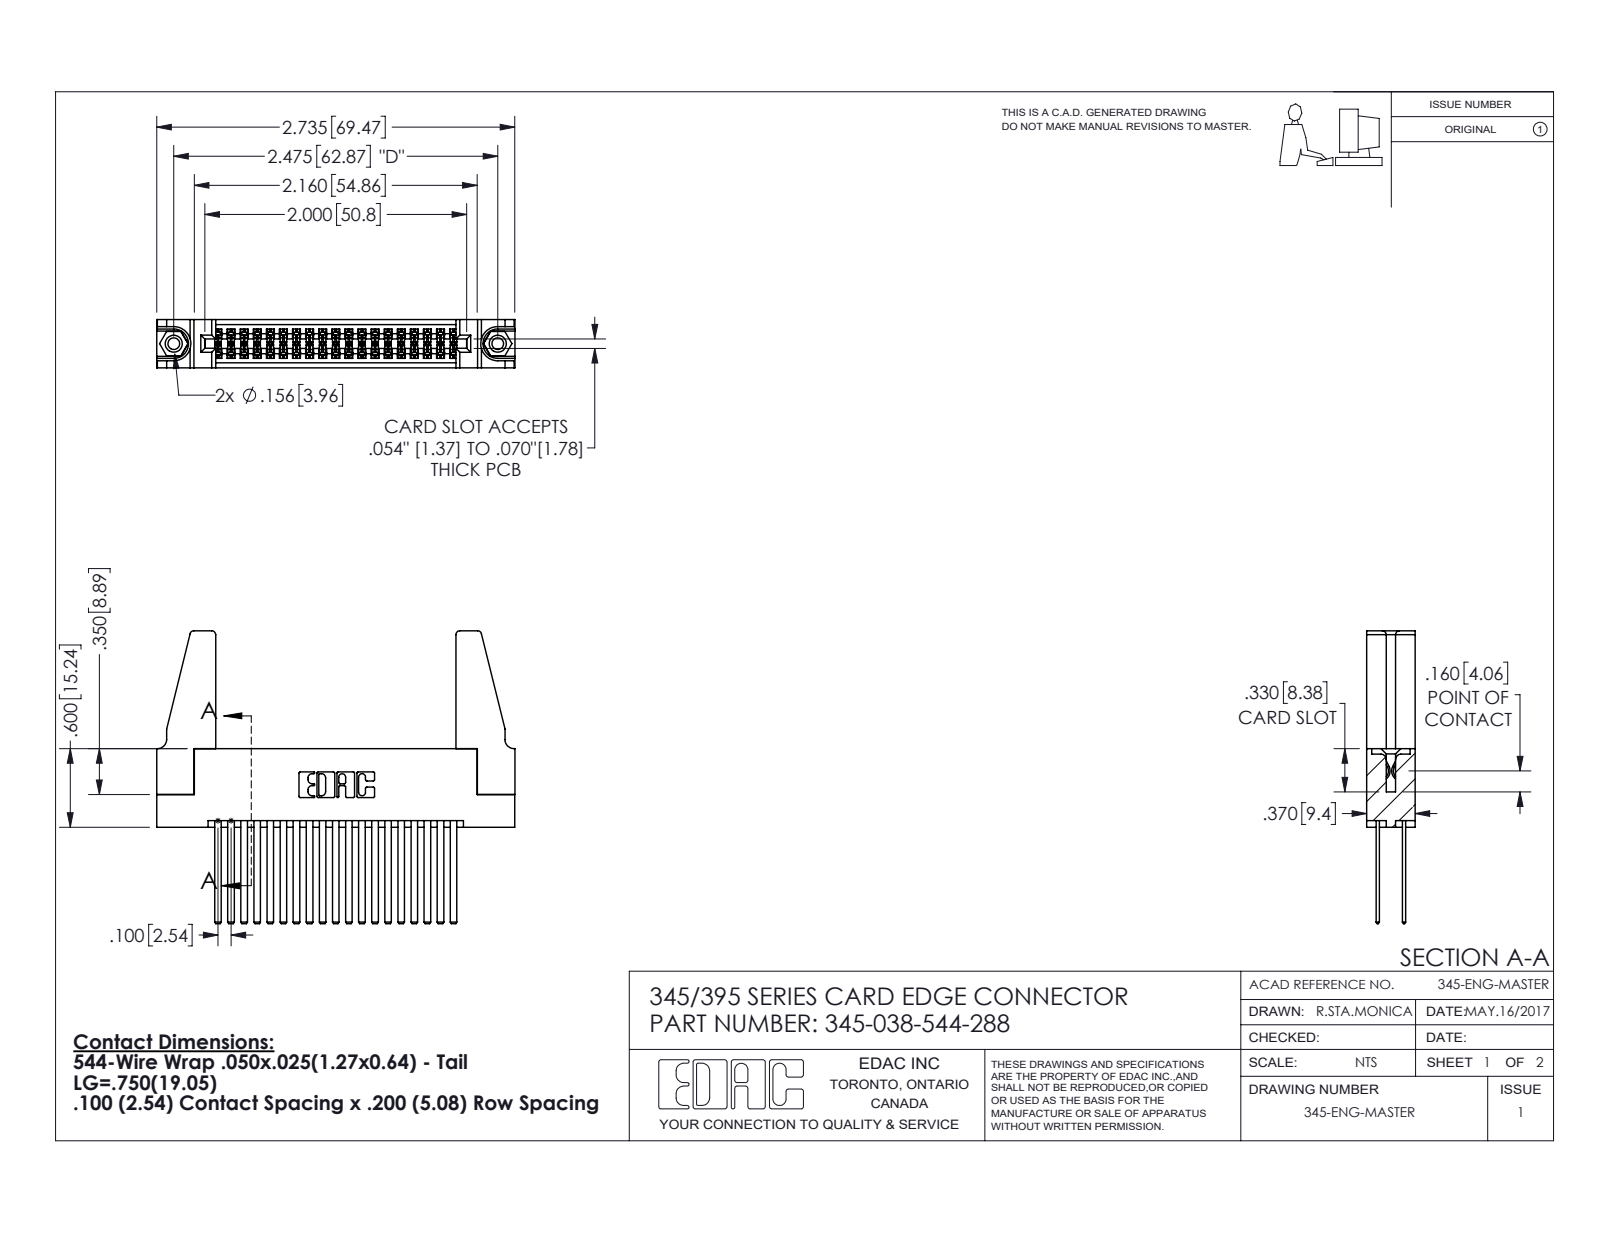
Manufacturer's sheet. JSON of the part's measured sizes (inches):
{"part_name": "345-250-001_345-250-001-102; 345-220-078_345-220-088; 345-292-001_345-293-144; 345 Part_Flush Mounting Lugs - 0.156 Dia-TH (+1 more)", "step_written_by": "SolidWorks 2016 (CONFIG_CONTROL_DESIGN)", "units": "inches", "bodies": {"solids": 43, "faces": 1922, "planar": 1254, "cylindrical": 652, "other": 16}, "overall_size": [2.736, 2.237, 0.37], "volume_in3": 0.63, "surface_area_in2": 22.77, "round_holes": [[0.089, 2], [0.125, 2], [0.156, 2], [0.064, 1]], "round_bosses_or_shafts": [[0.155, 2]], "partial_cylinders_radius": [[0.006, 57], [0.01, 22], [0.03, 8], [0.007, 6], [0.031, 6], [0.026, 3], [0.014, 2], [0.019, 2]], "face_to_face_distances": [0.072, 0.298, 0.2, 0.098, 0.272, 0.025, 0.37, 0.225, 0.175, 0.05], "hole_center_spacings": [0.27, 2.241, 2.475]}
